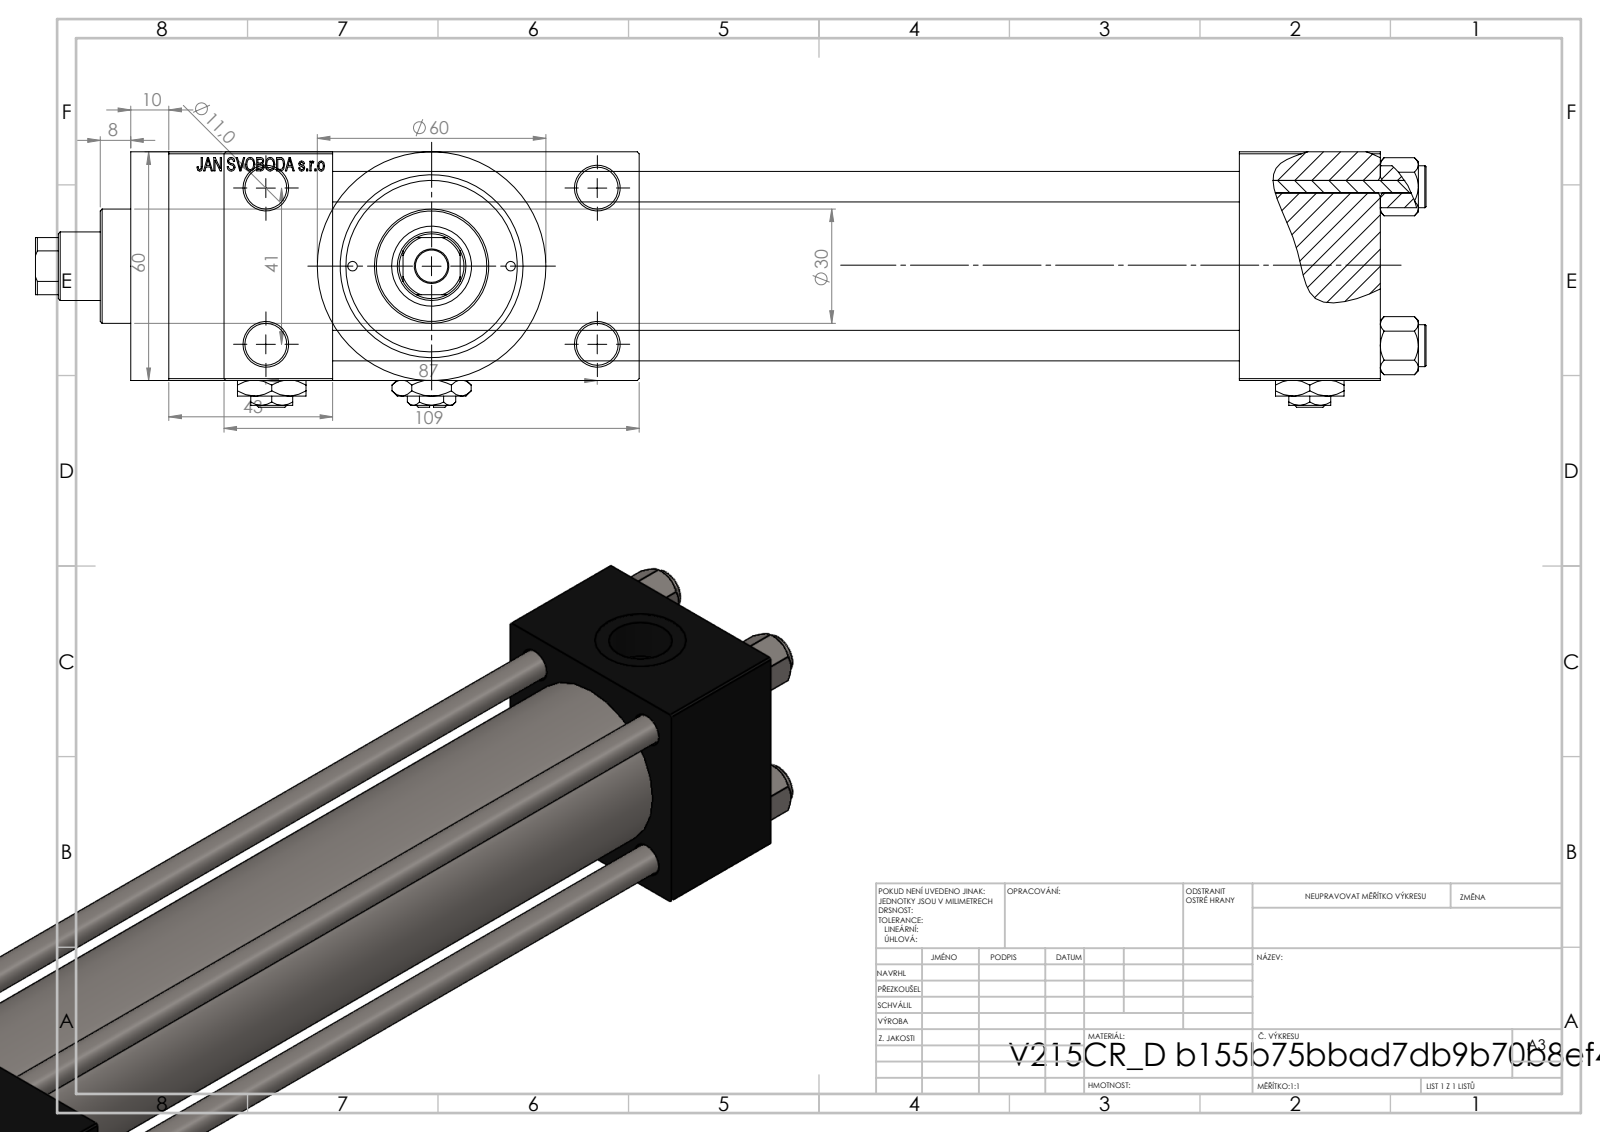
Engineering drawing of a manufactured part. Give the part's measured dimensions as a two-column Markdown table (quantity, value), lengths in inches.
| quantity | value |
| --- | --- |
| part name | Zatka_pro_OIL_PORT; NUT_M5_D; V215CR_VCP_D; V215CR_D_TYCINKA (+2 more) |
| STEP written by | SolidWorks 2019 (CONFIG_CONTROL_DESIGN) |
| units | inches |
| bodies | 13 solids, 1214 faces (548 planar, 104 cylindrical, 562 other) |
| overall size | 14.37 × 4.291 × 2.638 |
| volume | 40.91 in³ |
| surface area | 311.2 in² |
| round holes (diameter × count) | 0.315 × 4, 0.433 × 4, 0.098 × 2, 0.276 × 2, 0.656 × 2, 0.945 × 2, 0.335 × 1, 0.709 × 1, 0.827 × 1, 1.22 × 1, 1.575 × 1, 1.772 × 1 |
| round bosses / shafts (diameter × count) | 0.433 × 4, 2.362 × 1, 1.811 × 1, 1.181 × 1 |
| partial cylindrical surfaces (radius × count) | 0.335 × 1 |
| main face-to-face distances | 2.362, 0.965, 3.327, 9.37, 1.457, 10.827, 1.693, 12.52, 11.063, 4.291 |
| hole center spacings | 0.821, 0.892, 1.161, 1.206, 1.642, 1.832, 1.856, 1.893 |
